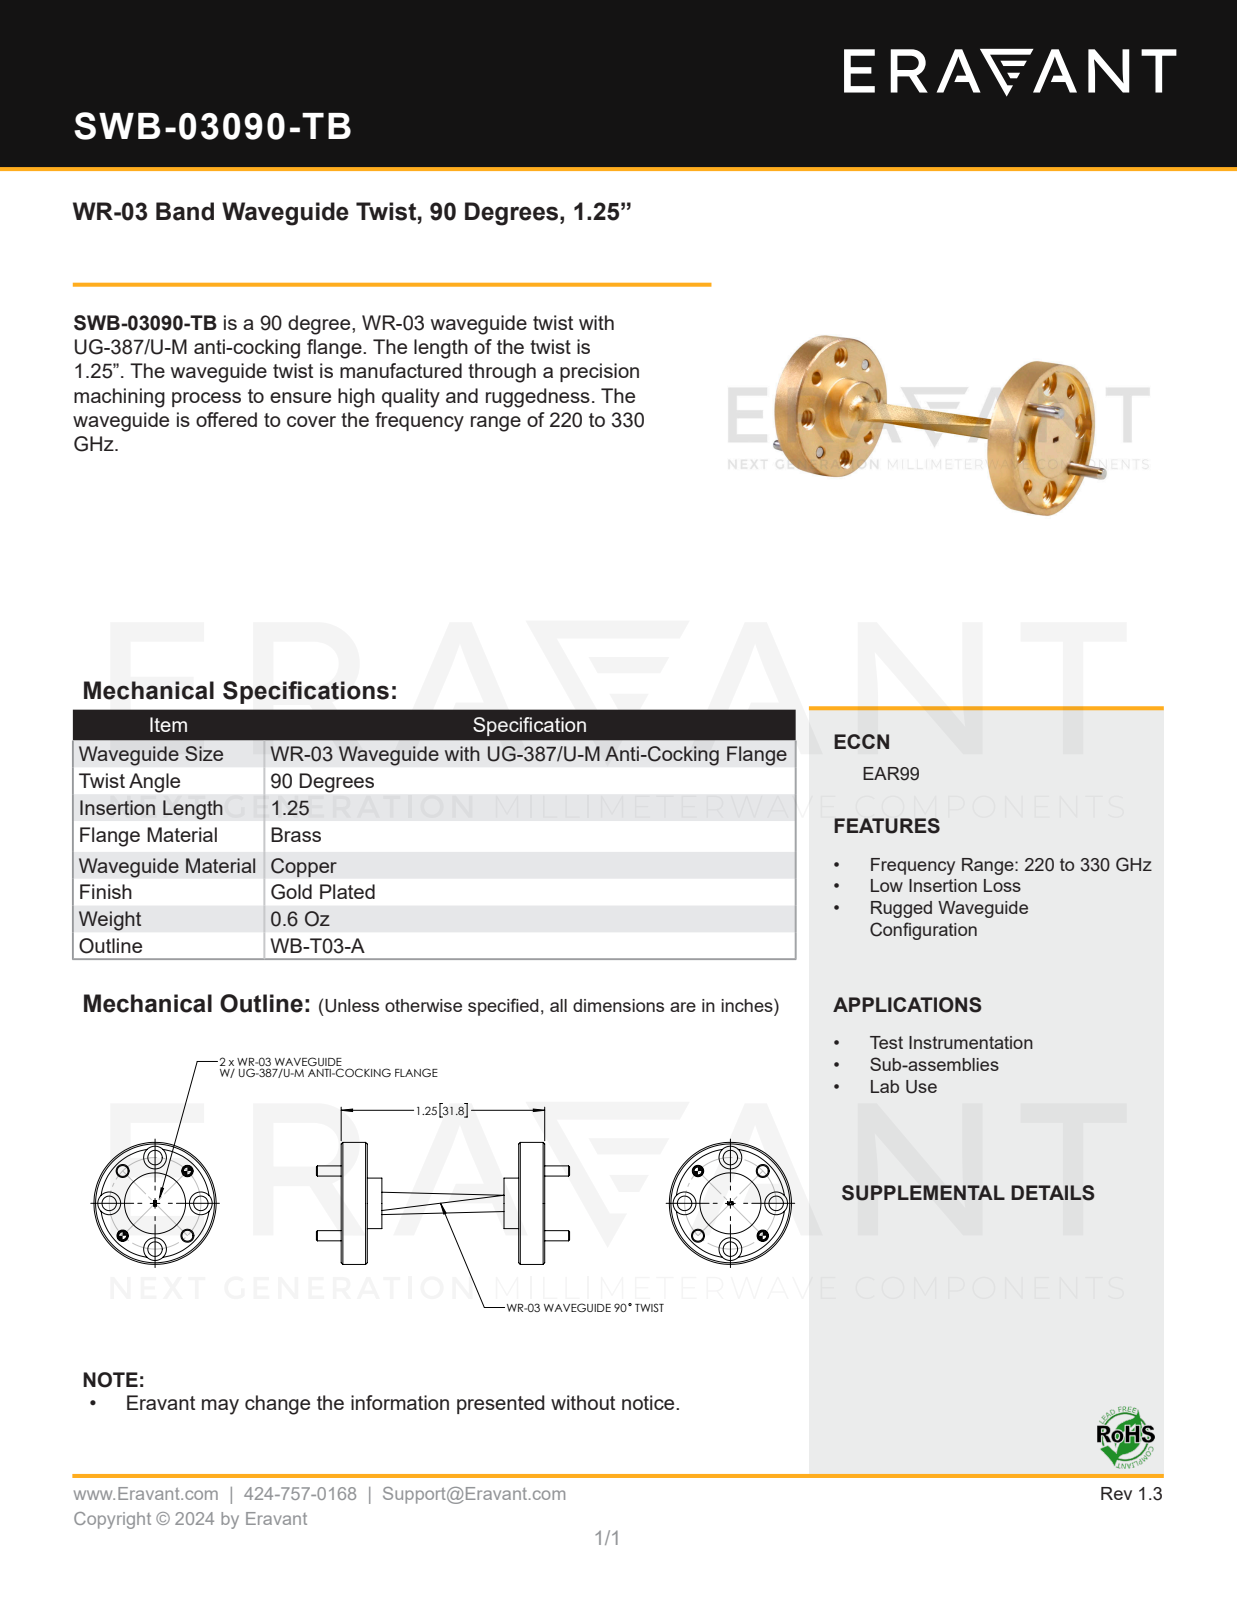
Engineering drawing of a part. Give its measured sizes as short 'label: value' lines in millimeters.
name: SWB-03090-TB
written by: SolidWorks 2021 (CONFIG_CONTROL_DESIGN)
unit: mm
bodies: 5 solids, 156 faces (36 planar, 76 cylindrical, 44 other)
size: 39.5 × 19.1 × 19.1
volume: 2 290 mm³; area: 2 419 mm²
holes: 4× ⌀2.3, 4× ⌀3.6, 2× ⌀1.5, 2× ⌀1.7, 1× ⌀17
bosses: 2× ⌀1.6, 1× ⌀19.1, 1× ⌀9.5, 1× ⌀7.9
face distances: 4.1, 27.7, 0.8, 31, 3.3, 26.9, 23.6, 31.8, 30.2, 6.4
hole spacings: 5.5, 10.1, 7.1, 13.2, 13.2, 7.1, 14.3, 14.3
